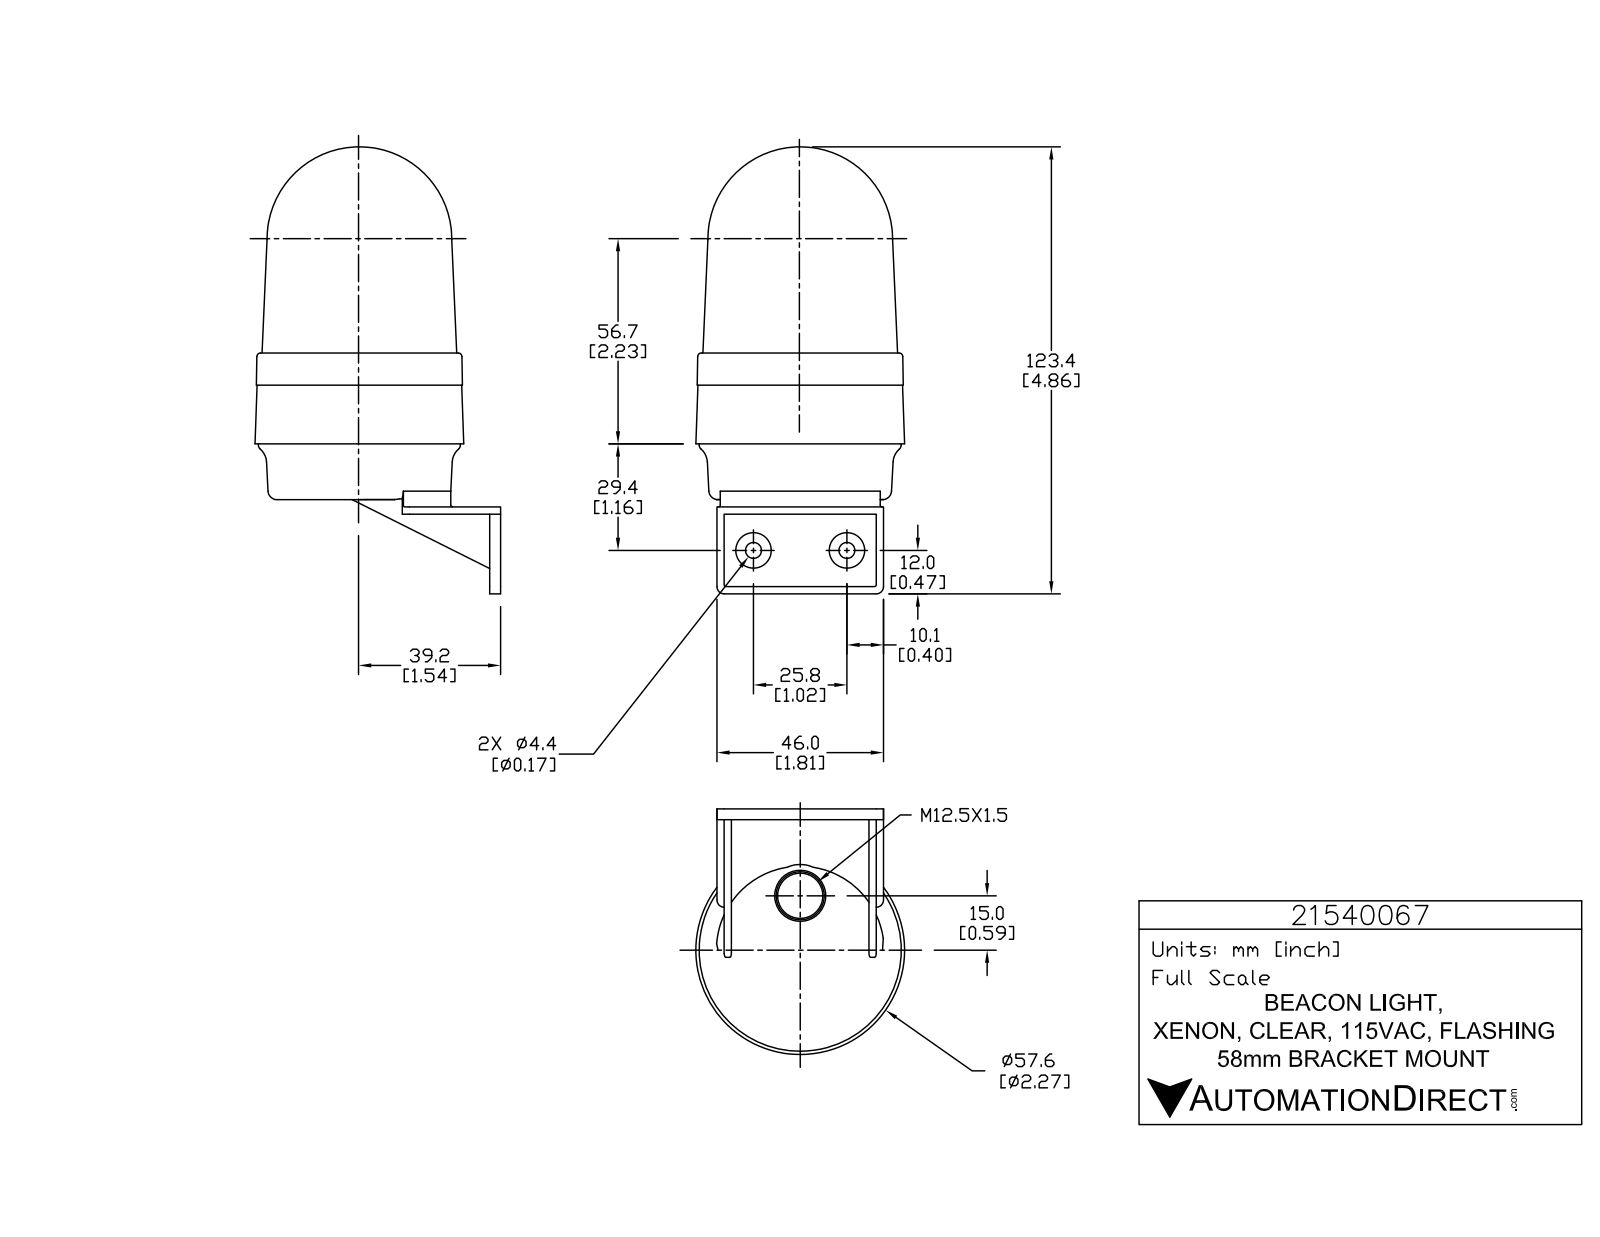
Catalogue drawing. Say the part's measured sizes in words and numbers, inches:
The part is named "21540067". Its 3-D file was written by "SolidWorks 2015 (AUTOMOTIVE_DESIGN)". It is 1 solid with 828 faces: 551 planar, 179 cylindrical and 98 other. Overall it measures 4.858 by 2.852 by 2.407 inches. Its volume is 12.43 cubic inches and its surface area 37.49 square inches. Round holes: 3 of diameter 0.039, 2 of diameter 0.173. Round bosses or shafts: 3 of diameter 0.226, 3 of diameter 0.056, 2 of diameter 0.386, 1 of diameter 2.197. Partial cylindrical surfaces (rounded edges, fillets, slot ends): 6 of radius 0.008, 6 of radius 0.008, 6 of radius 0.008, 6 of radius 0.02, 6 of radius 0.131, 4 of radius 0.079, 3 of radius 0.004, 3 of radius 0.005. The main face-to-face distances are 0.079, 0.157, 1.575, 1.654, 0.039, 0.118, 1.496, 0.866, 0.945, 0.764. The hole center spacings are 1.016.
